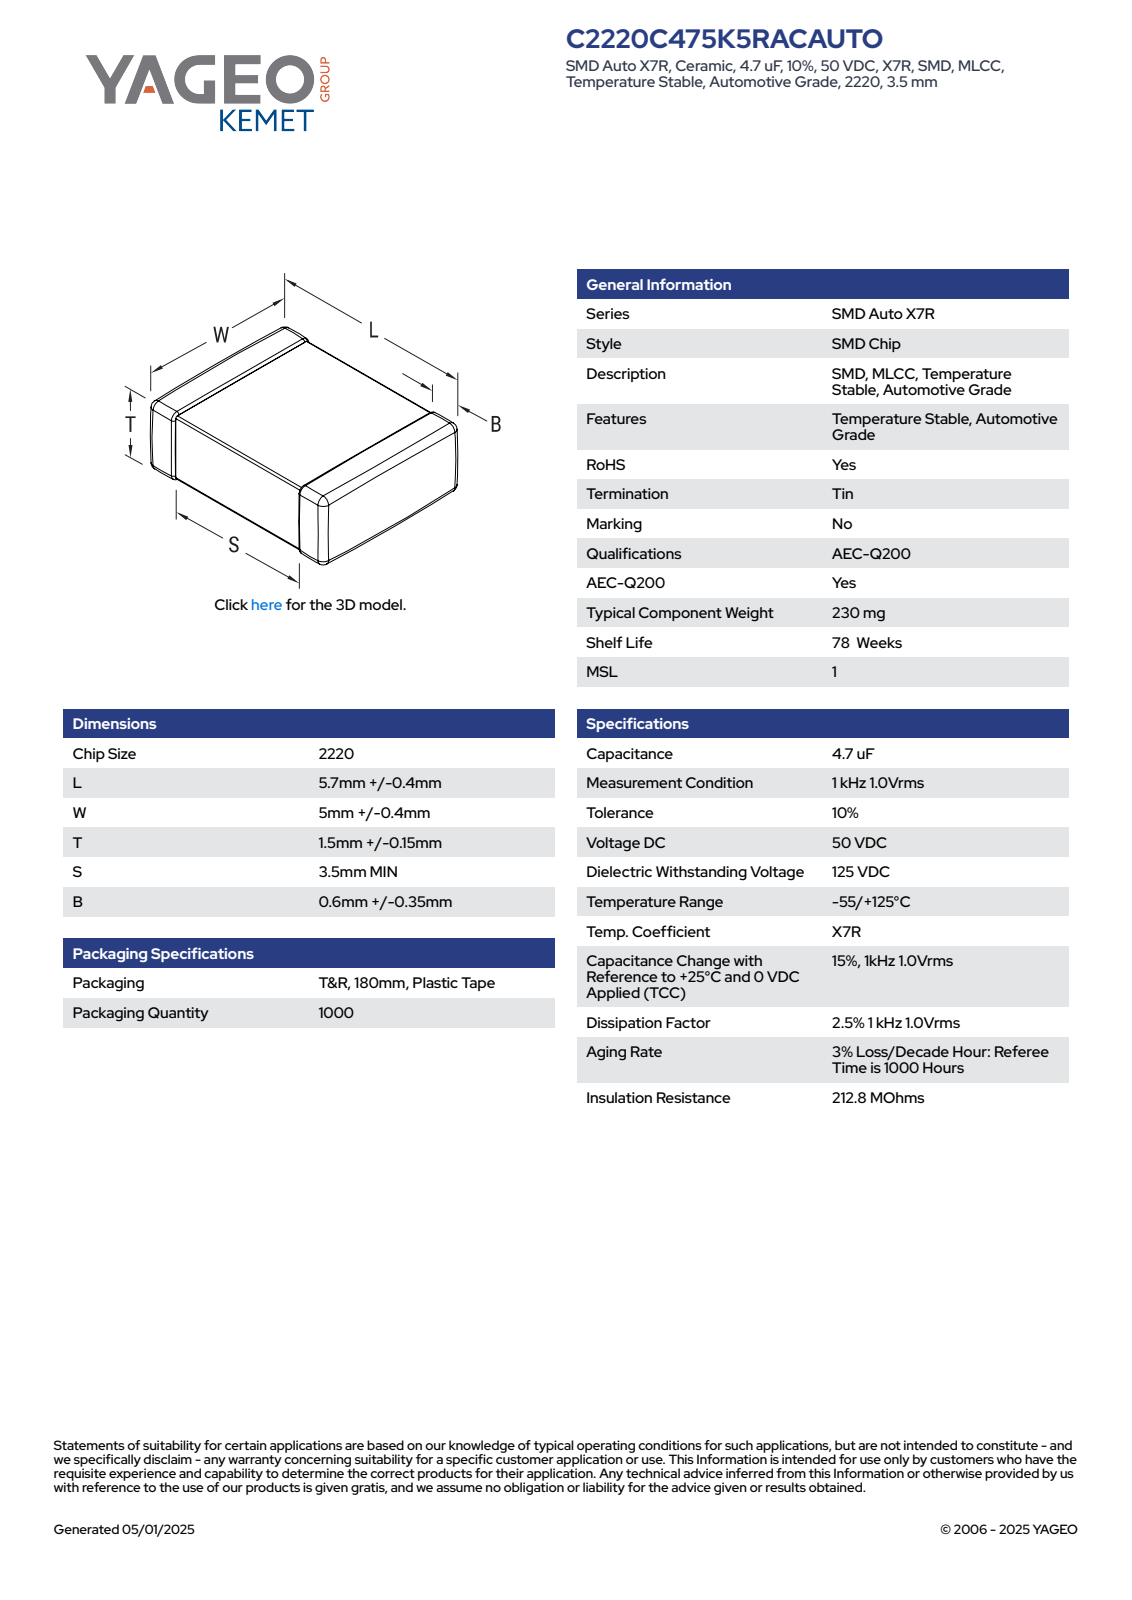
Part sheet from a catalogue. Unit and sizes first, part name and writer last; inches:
Units: inches
Overall size (bounding box): 0.24 × 0.213 × 0.065
Partial cylindrical surfaces — rounded edges, fillets, slot ends (radius × count): R0.004 ×24
Main face-to-face distances: 0.056, 0.061, 0.065, 0.24, 0.204, 0.208, 0.213, 0.098, 0.142, 0.13
Volume: 0.003 in³ · Surface area: 0.16 in²
Bodies: 4 solids, 125 faces (71 planar, 38 cylindrical, 16 other)
Part name (STEP PRODUCT): CCS_CCSTD_2220_L6.1W5.4T1.65B0.6
STEP written by: SolidWorks 2021 (AUTOMOTIVE_DESIGN)
